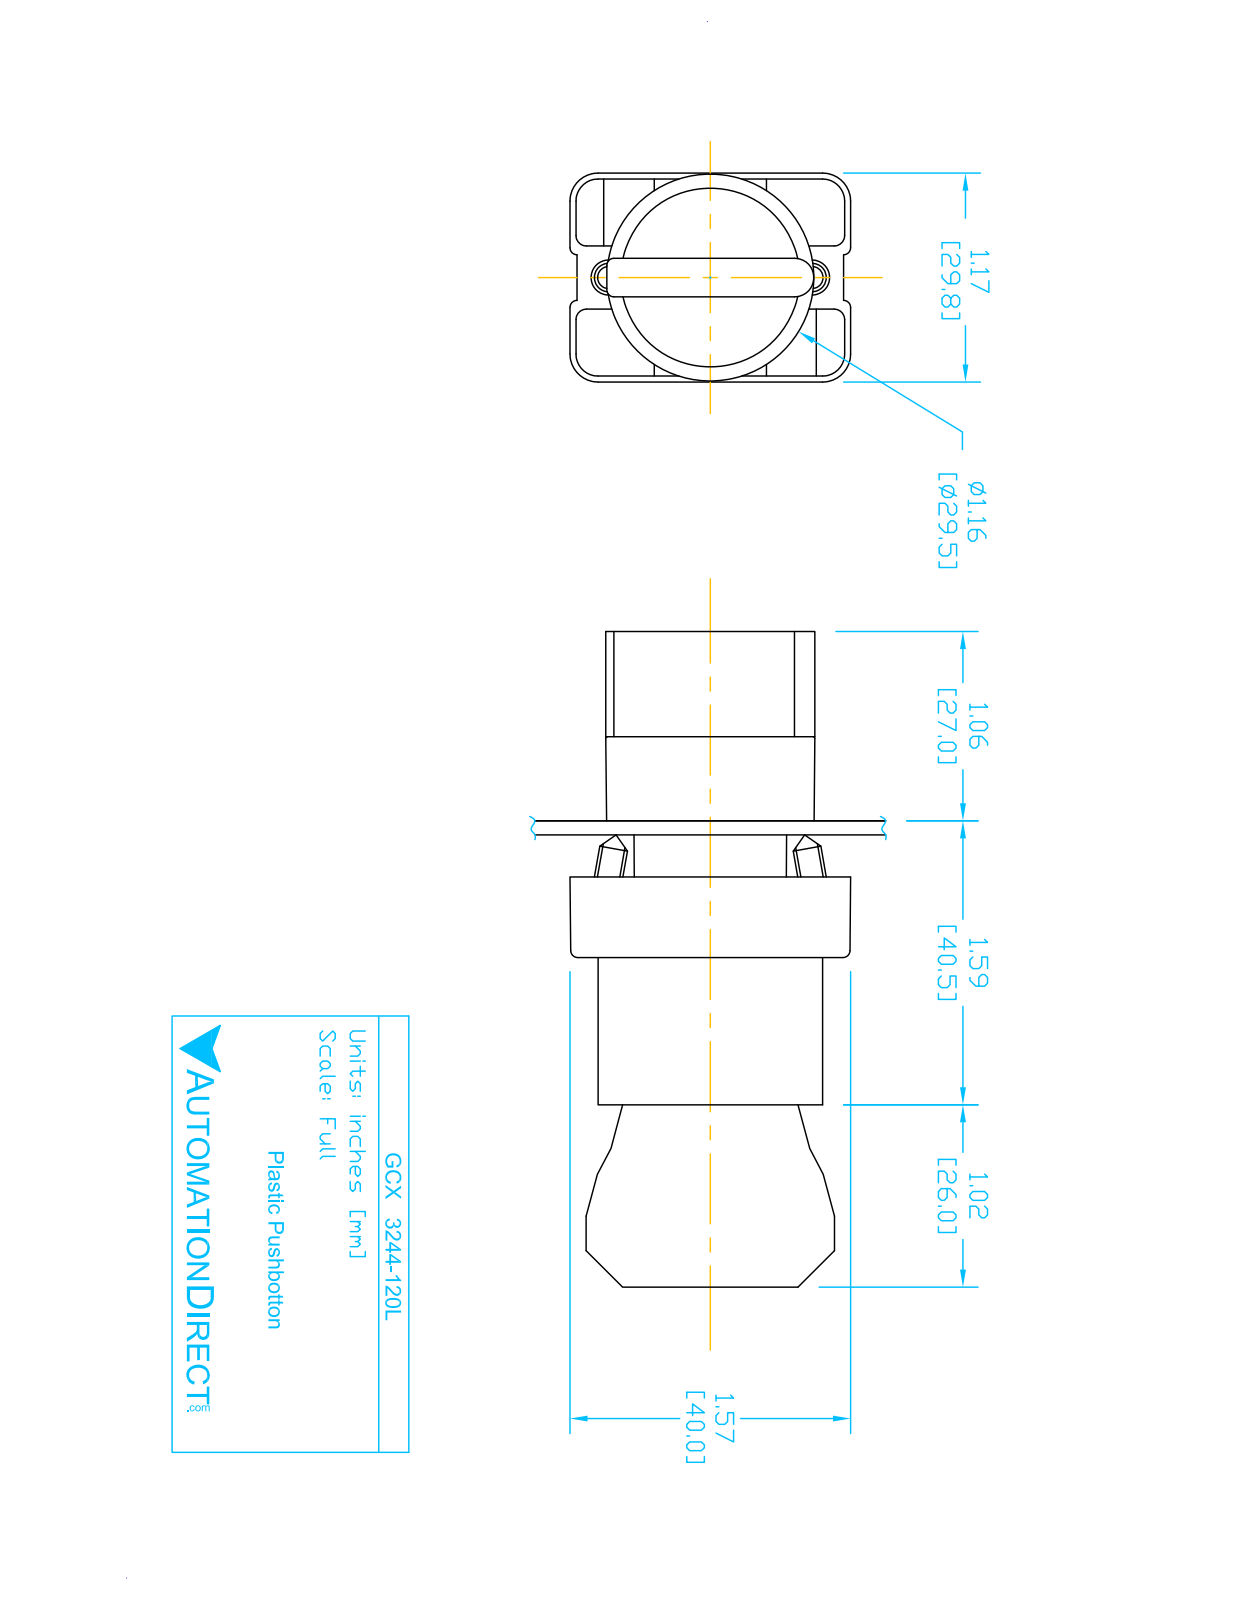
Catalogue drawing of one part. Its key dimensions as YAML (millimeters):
part_name: "ECX1050; ecx1040; GCX3244-120L; GCX3244L OPERATOR (+1 more)"
step_written_by: "SolidWorks 2016 (AUTOMOTIVE_DESIGN)"
units: millimeters
bodies: {solids: 8, faces: 445, planar: 263, cylindrical: 151, other: 31}
overall_size: [92.8, 40.2, 29.9]
volume: 45870
surface_area: 25160
round_holes:
  - {diameter: 2, count: 2}
  - {diameter: 3.1, count: 2}
  - {diameter: 3.3, count: 2}
  - {diameter: 2.2, count: 1}
  - {diameter: 5, count: 1}
  - {diameter: 11.9, count: 1}
  - {diameter: 22.3, count: 1}
  - {diameter: 22.6, count: 1}
  - {diameter: 26, count: 1}
round_bosses_or_shafts:
  - {diameter: 4, count: 4}
  - {diameter: 29.8, count: 1}
  - {diameter: 25.5, count: 1}
  - {diameter: 24, count: 1}
  - {diameter: 21.7, count: 1}
  - {diameter: 19.8, count: 1}
  - {diameter: 12.8, count: 1}
partial_cylinders:
  - {radius: 1.5, count: 24}
  - {radius: 1, count: 12}
  - {radius: 3.1, count: 12}
  - {radius: 4, count: 12}
  - {radius: 1, count: 9}
  - {radius: 3.3, count: 2}
  - {radius: 0.5, count: 1}
  - {radius: 1.6, count: 1}
face_to_face_distances: [21, 51.3, 30.3, 14.7, 31.6, 29.7, 12, 11.9, 0.8, 0.8]
hole_center_spacings: [6, 13.8, 12, 12.4]
